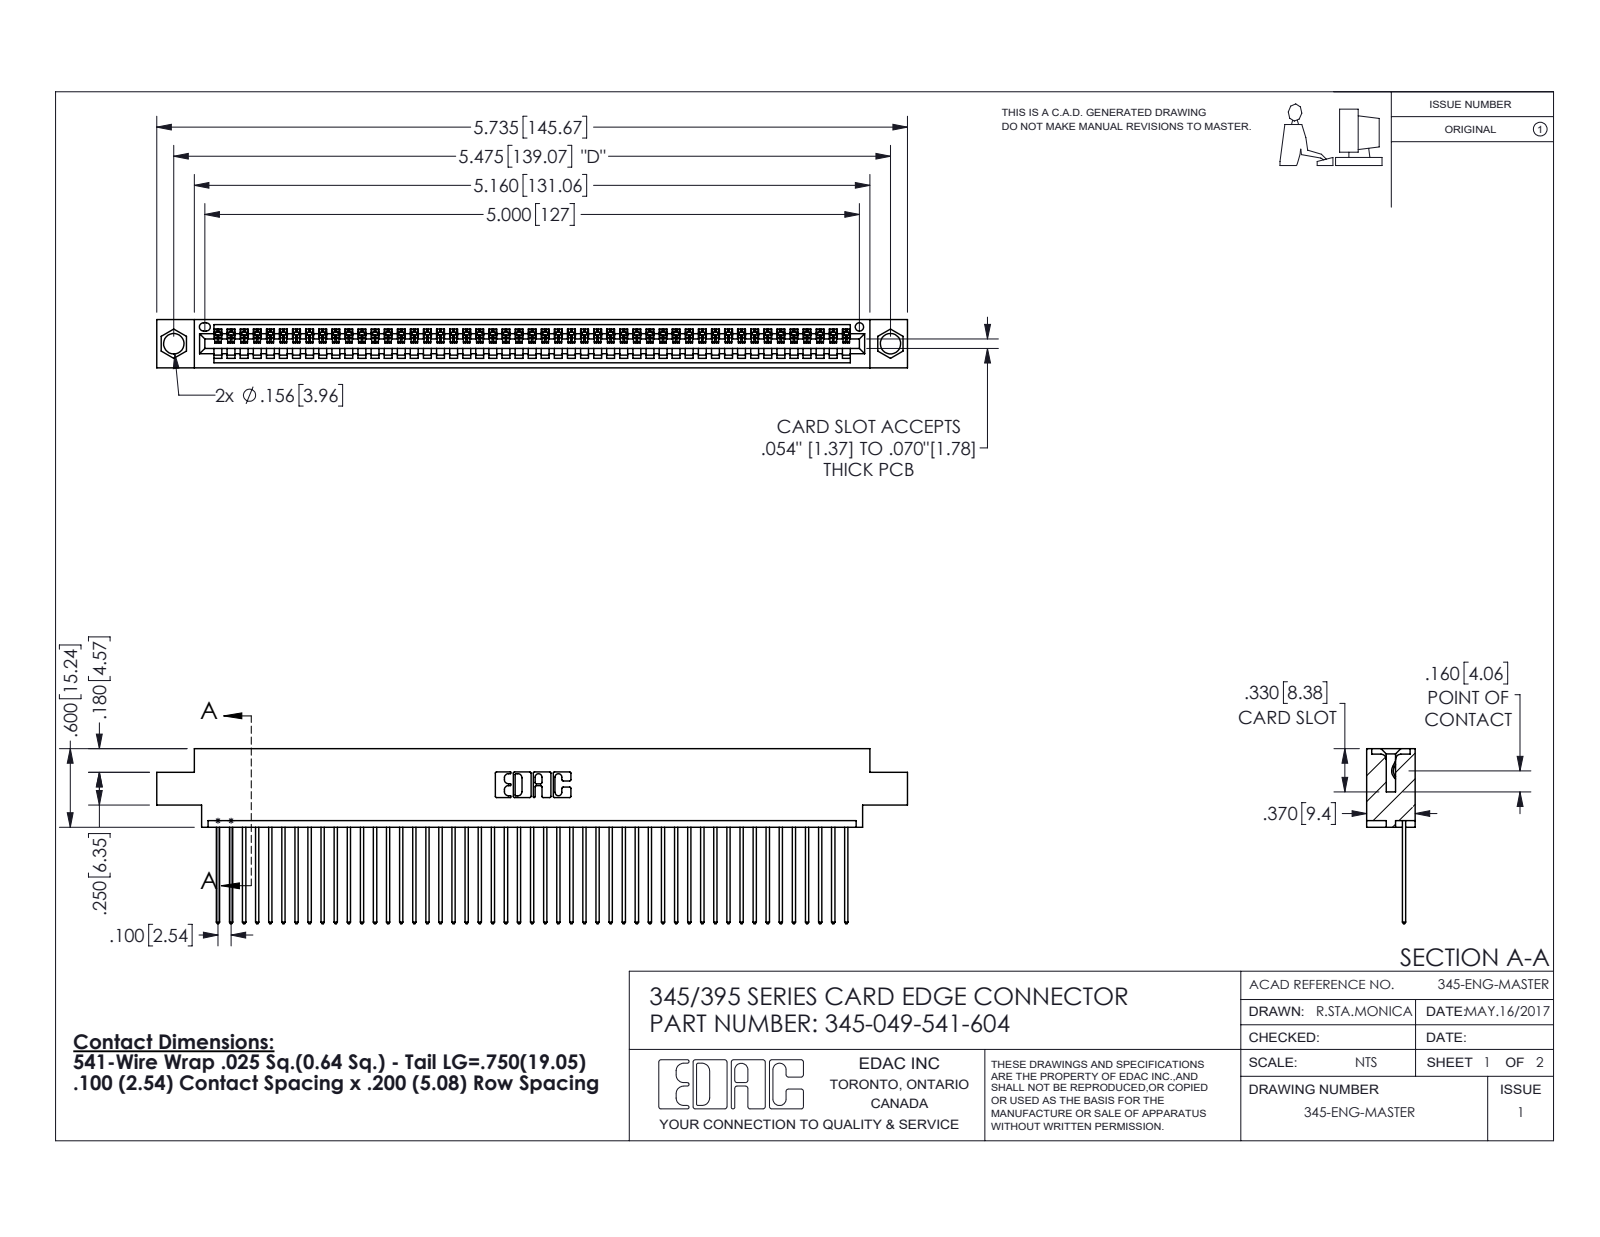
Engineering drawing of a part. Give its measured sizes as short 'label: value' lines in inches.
name: 345 Part_0.170 Offset - 0.156 Dia-TH; 345-292-001_345-293-141; 345-049-541-604
written by: SolidWorks 2016 (CONFIG_CONTROL_DESIGN)
unit: in
bodies: 50 solids, 2972 faces (2044 planar, 928 cylindrical, 0 other)
size: 5.735 × 1.337 × 0.37
volume: 0.845 in³; area: 30.06 in²
holes: 2× ⌀0.156, 1× ⌀0.064
rounds: 98× R0.006, 98× R0.01, 22× R0.01, 6× R0.007, 6× R0.031, 3× R0.026, 2× R0.031, 2× R0.04
face distances: 0.072, 0.298, 0.37, 0.098, 0.272, 0.025, 0.2, 0.225, 0.175, 0.149
hole spacings: 0.27, 5.239, 5.475
